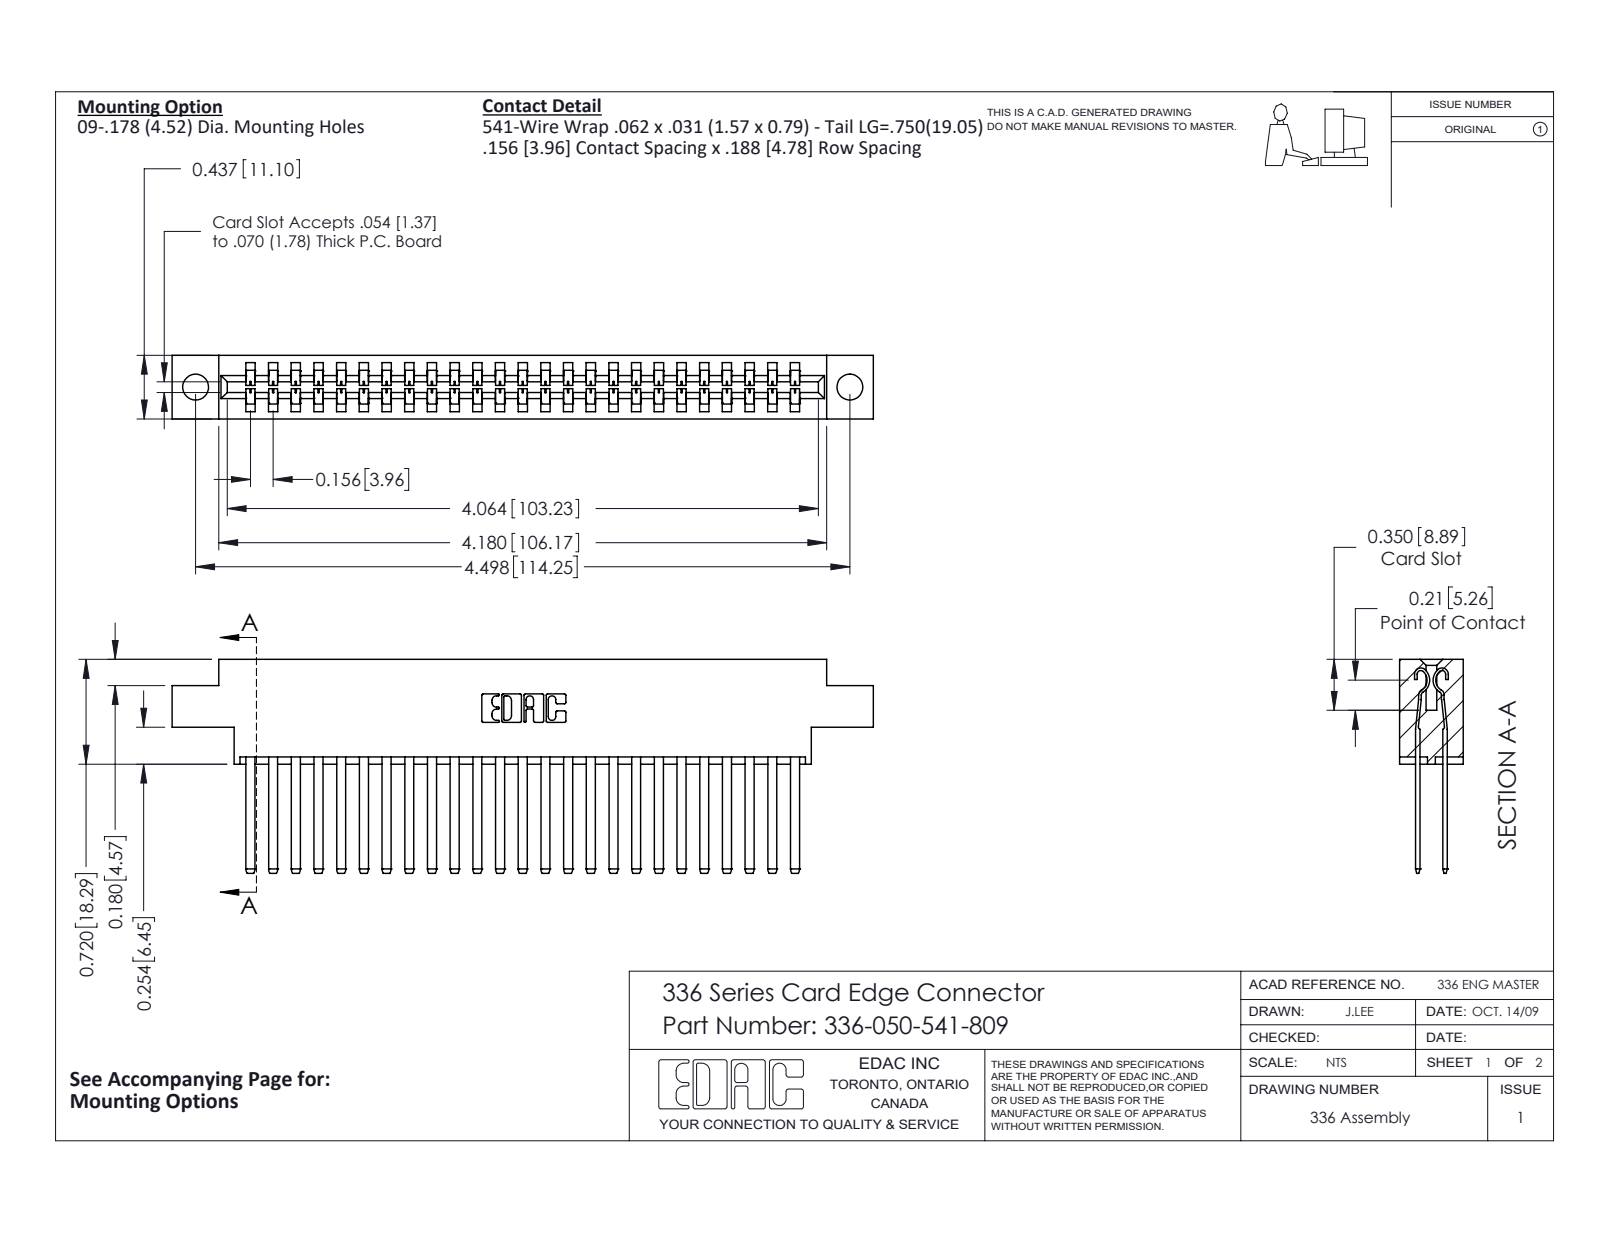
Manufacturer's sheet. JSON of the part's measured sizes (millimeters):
{"part_name": "336-290-001_336-290-541; 336-050-541-809; 336 Part_Offset - .178 Dia - TH", "step_written_by": "SolidWorks 2020 (CONFIG_CONTROL_DESIGN)", "units": "millimeters", "bodies": {"solids": 51, "faces": 2218, "planar": 1374, "cylindrical": 844, "other": 0}, "overall_size": [122.5, 37.3, 11.1], "volume_mm3": 18220, "surface_area_mm2": 22940, "round_holes": [[4.5, 2]], "partial_cylinders_radius": [[0.1, 100], [1.4, 50], [0.3, 22], [0.2, 6], [0.8, 6], [0.6, 4], [1, 4], [0.7, 3]], "face_to_face_distances": [4.8, 8.3, 3.6, 7.5, 2.8, 0.8, 11.1, 0.8, 4.6, 6.5], "hole_center_spacings": [114.2]}
